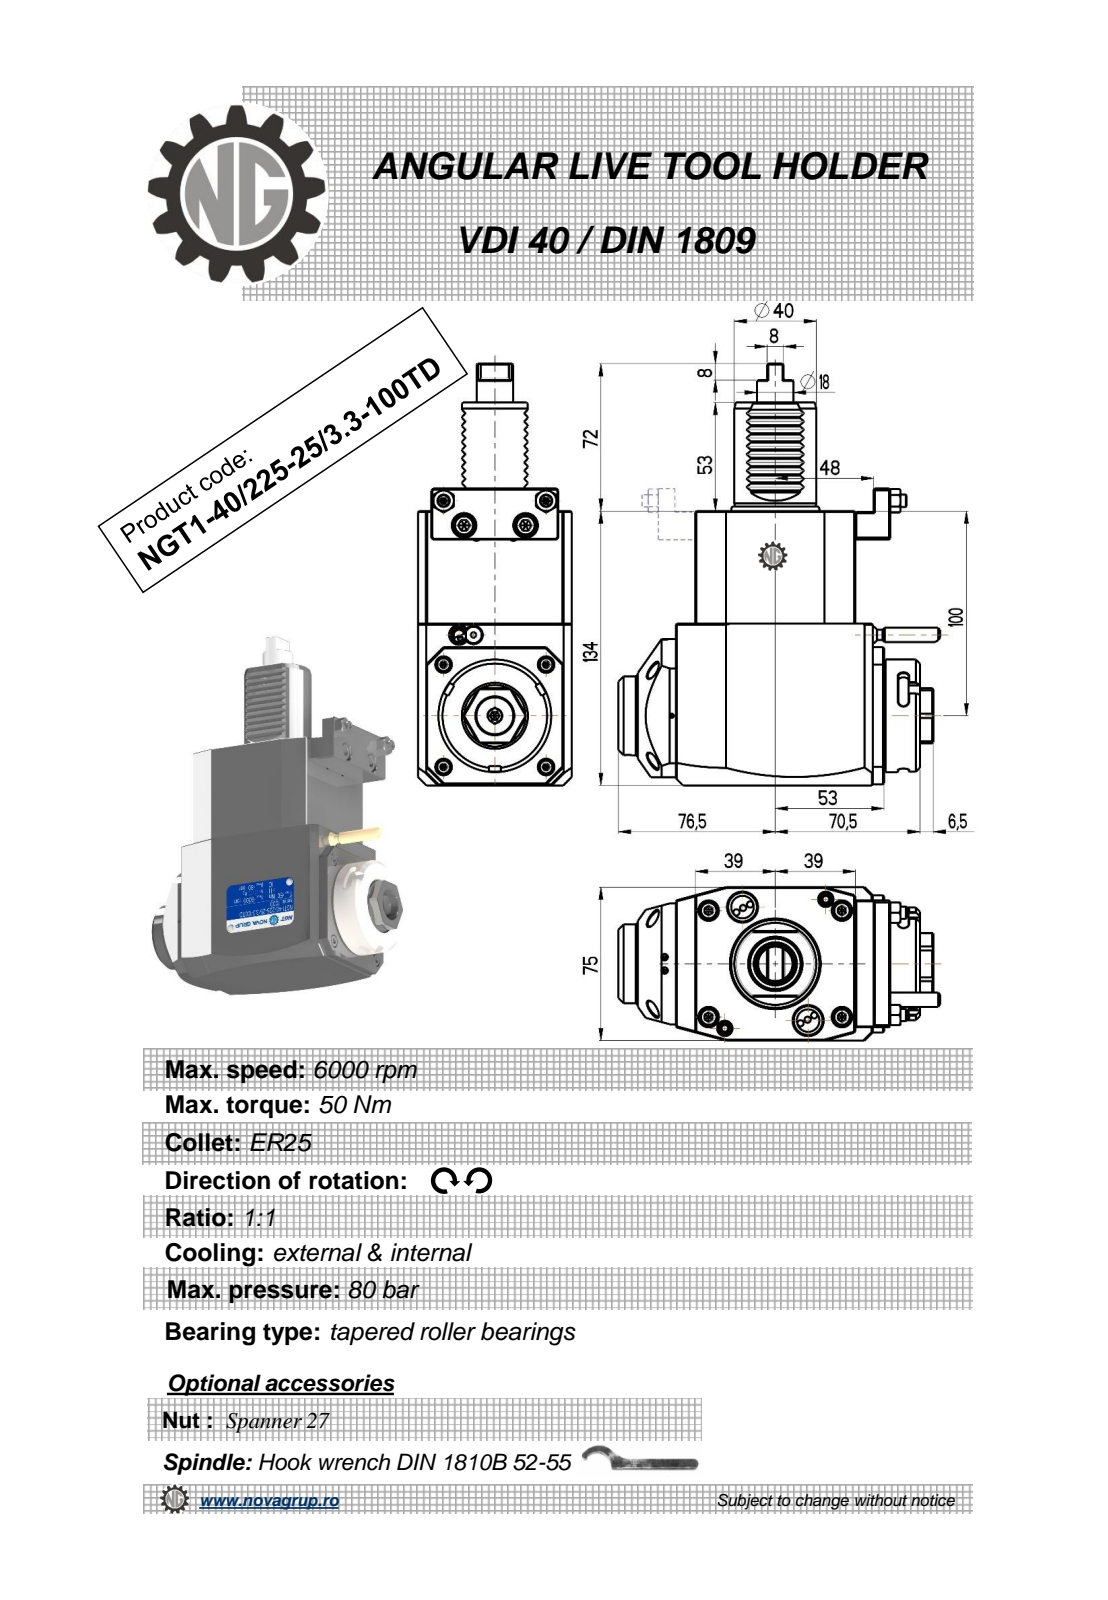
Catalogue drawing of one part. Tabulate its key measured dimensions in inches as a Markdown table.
| quantity | value |
| --- | --- |
| part name | NGT1_40_225_25_3_3_100TD |
| STEP written by | PRO/ENGINEER BY PARAMETRIC TECHNOLOGY CORPORATION, 2010280 (CONFIG_CONTROL_DESIGN) |
| units | inches |
| bodies | 1 solid, 426 faces (223 planar, 95 cylindrical, 108 other) |
| overall size | 8.11 × 6.174 × 2.953 |
| volume | 66.03 in³ |
| surface area | 122.1 in² |
| round holes (diameter × count) | 0.079 × 2, 0.102 × 2, 0.098 × 1, 0.118 × 1, 0.709 × 1 |
| round bosses / shafts (diameter × count) | 1.575 × 2, 0.236 × 2, 2.165 × 1, 1.89 × 1, 1.516 × 1, 0.701 × 1, 0.315 × 1, 0.276 × 1 |
| partial cylindrical surfaces (radius × count) | 0.012 × 20, 0.012 × 10, 0.008 × 6, 0.098 × 6, 0.031 × 2, 7.087 × 2, 0.591 × 1, 0.965 × 1 |
| main face-to-face distances | 2.953, 5.276, 0.551, 3.071, 3.622, 0.02, 0.689, 0.669, 0.571, 4.311 |
| hole center spacings | 0.561, 1.122, 1.56, 1.701, 1.995 |
